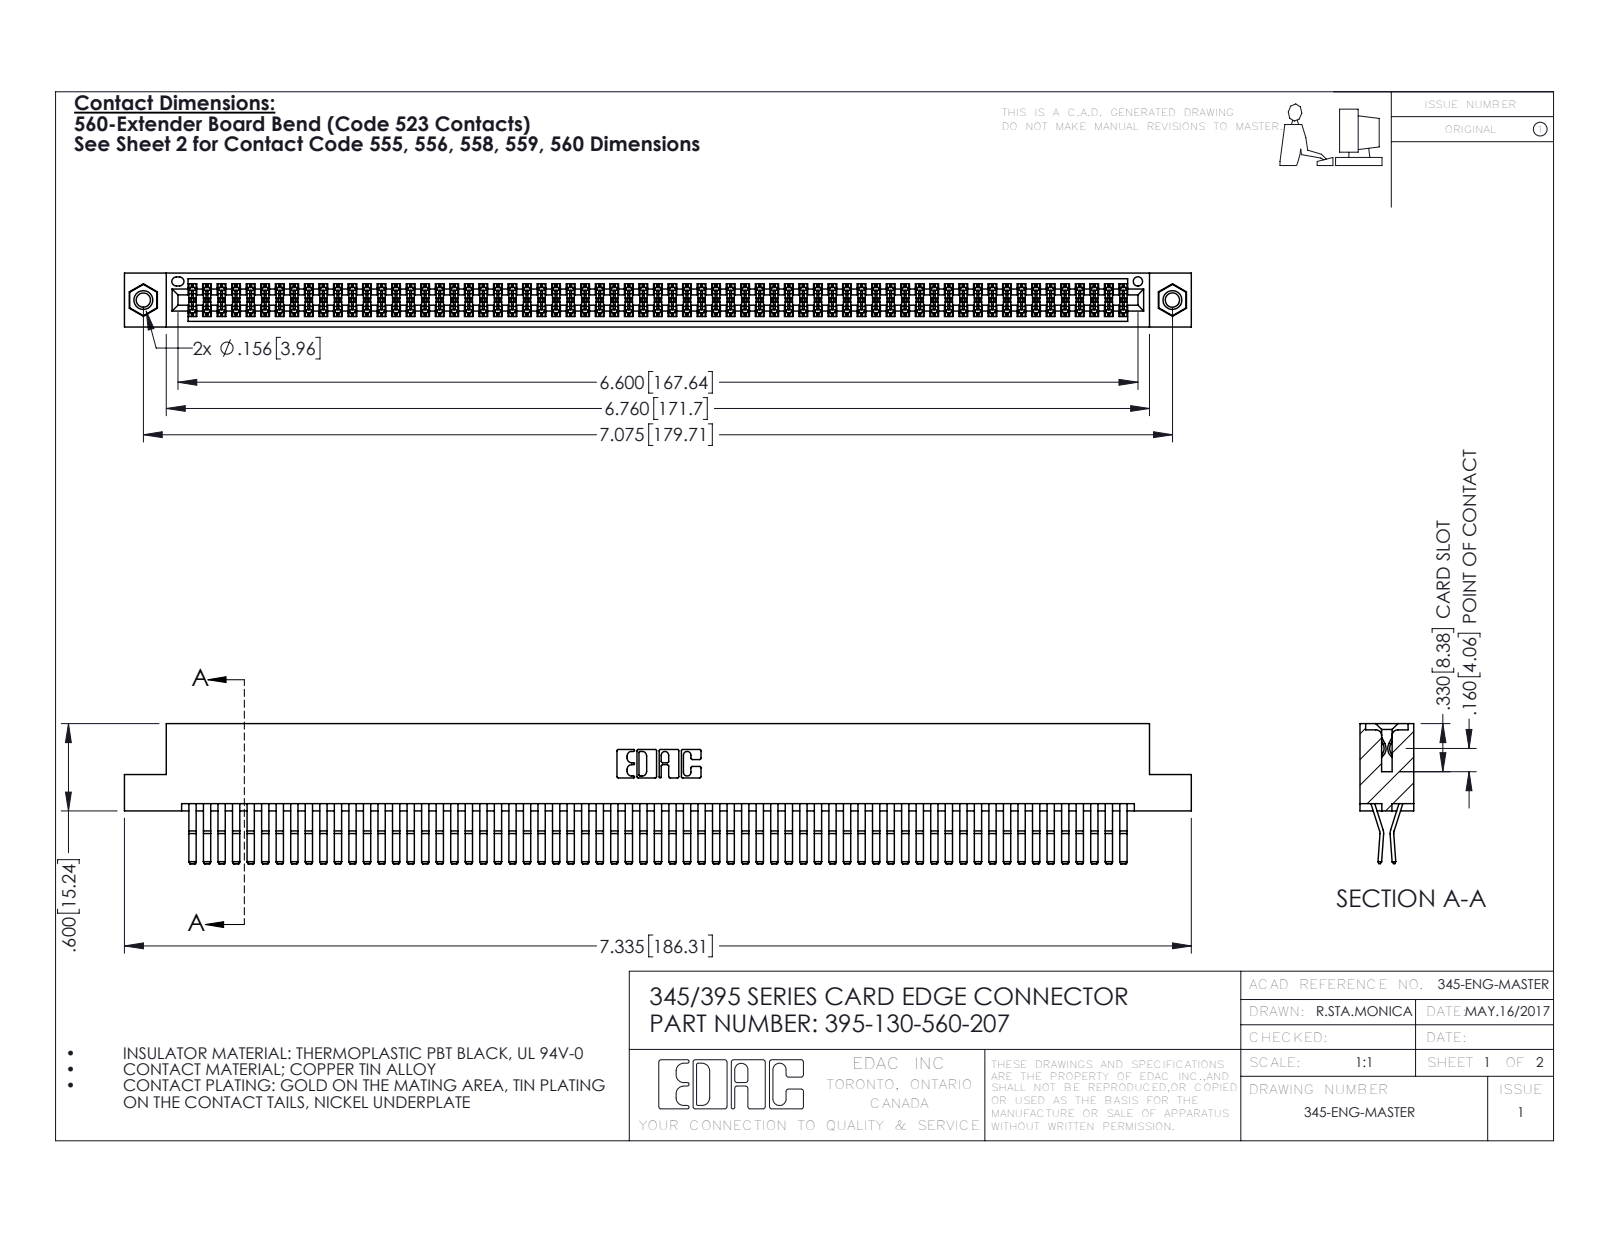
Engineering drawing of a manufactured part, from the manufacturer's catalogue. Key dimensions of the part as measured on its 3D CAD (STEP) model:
Part name (STEP PRODUCT): 395-130-560-207; 345 Part_Flush Mounting Lugs - 0.156 Dia-TI; 345-250-001_345-250-005-103; 345-292-001_560 Tail
STEP written by: SolidWorks 2016 (CONFIG_CONTROL_DESIGN)
Units: inches
Bodies: 133 solids, 6946 faces (4402 planar, 2528 cylindrical, 16 other)
Overall size (bounding box): 7.335 × 0.962 × 0.37
Volume: 1.169 in³ · Surface area: 48.01 in²
Round holes (diameter × count): ⌀0.098 ×2, ⌀0.125 ×2, ⌀0.156 ×2, ⌀0.064 ×1
Round bosses / shafts (diameter × count): ⌀0.155 ×2
Partial cylindrical surfaces — rounded edges, fillets, slot ends (radius × count): R0.006 ×195, R0.01 ×22, R0.007 ×6, R0.031 ×6, R0.026 ×3, R0.01 ×2, R0.014 ×2, R0.019 ×2
Main face-to-face distances: 0.025, 0.072, 0.298, 0.37, 0.2, 0.098, 0.272, 0.225, 0.175, 0.149
Hole centre spacings: 0.27, 6.839, 7.075
